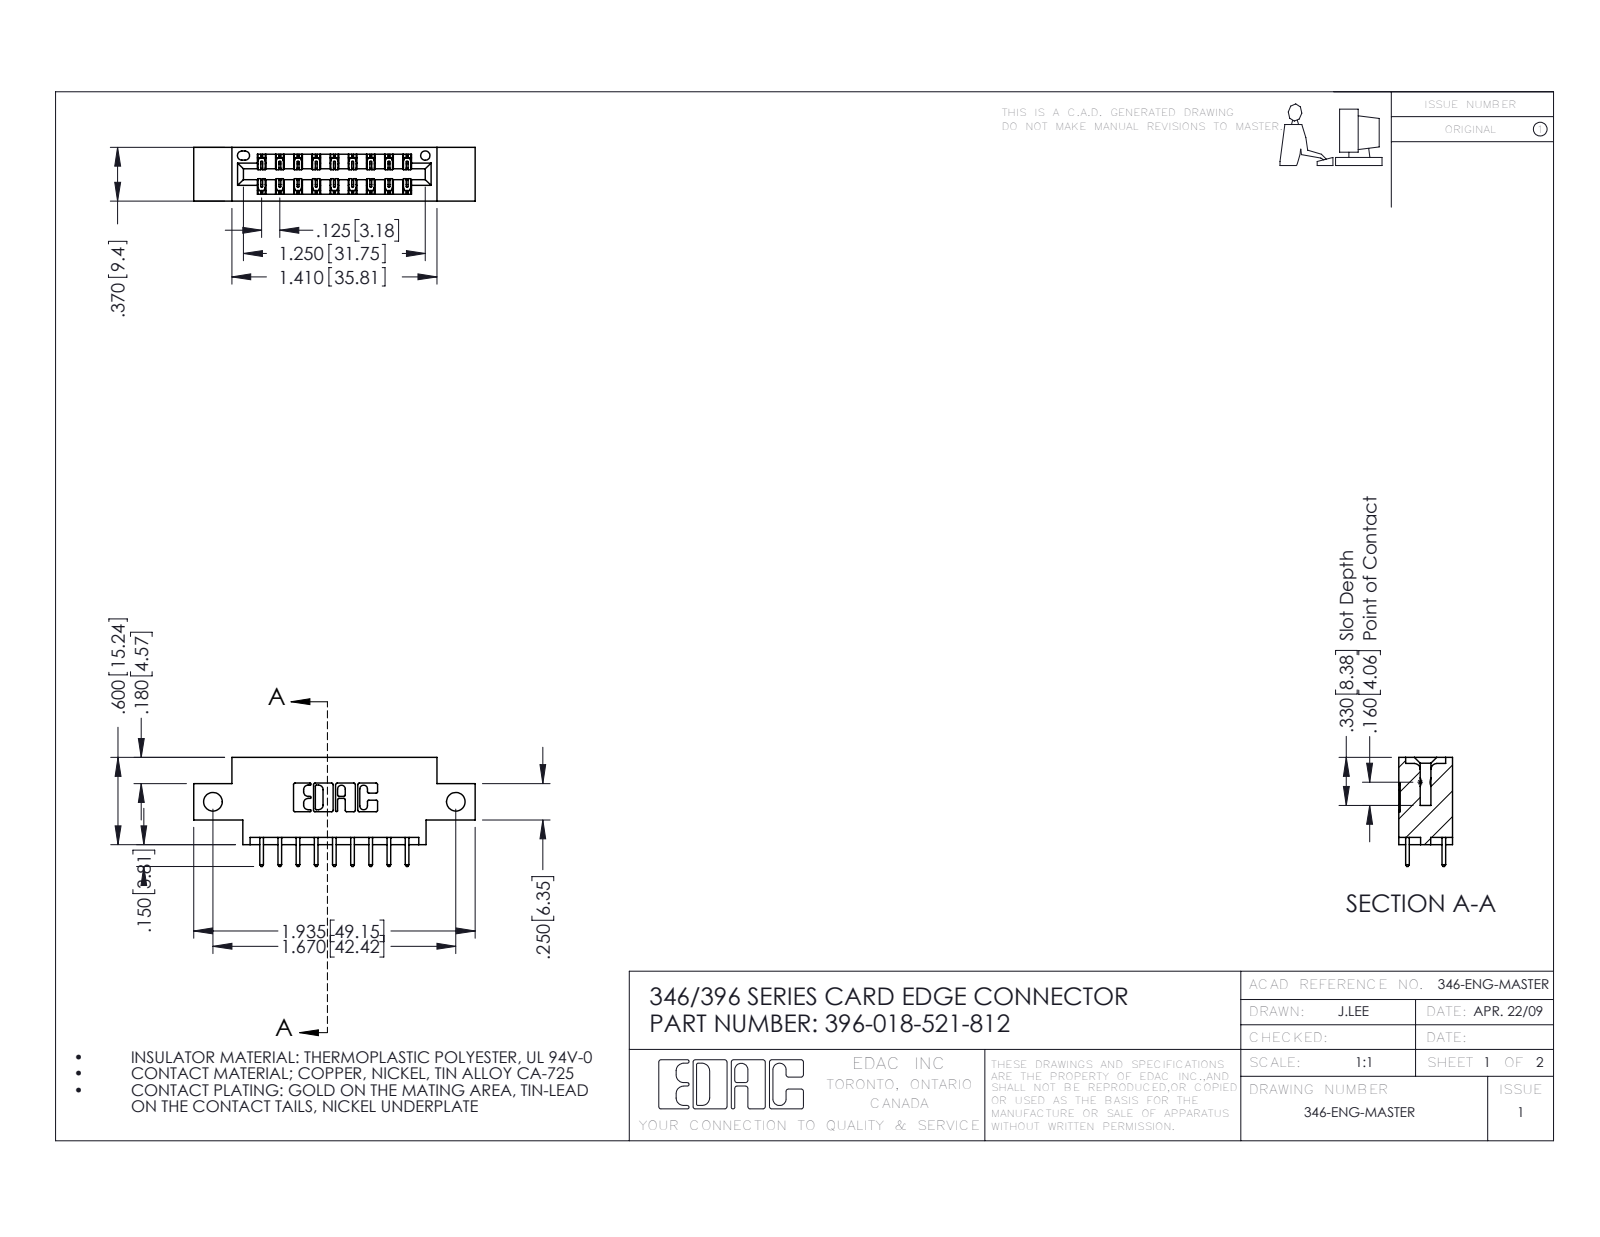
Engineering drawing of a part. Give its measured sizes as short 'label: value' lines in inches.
name: 396-018-521-812; 345-292-001_345-293-121; 346 Part_0.170 Offset - Side Mount
written by: SolidWorks 2016 (CONFIG_CONTROL_DESIGN)
unit: in
bodies: 19 solids, 1062 faces (710 planar, 352 cylindrical, 0 other)
size: 1.935 × 0.75 × 0.37
volume: 0.262 in³; area: 8.319 in²
holes: 2× ⌀0.128, 1× ⌀0.064
rounds: 27× R0.006, 22× R0.01, 18× R0.01, 6× R0.007, 6× R0.031, 3× R0.026, 2× R0.014, 2× R0.022
face distances: 0.25, 0.37, 0.048, 0.322, 0.072, 0.298, 0.025, 0.275, 0.148, 0.222
hole spacings: 1.67
